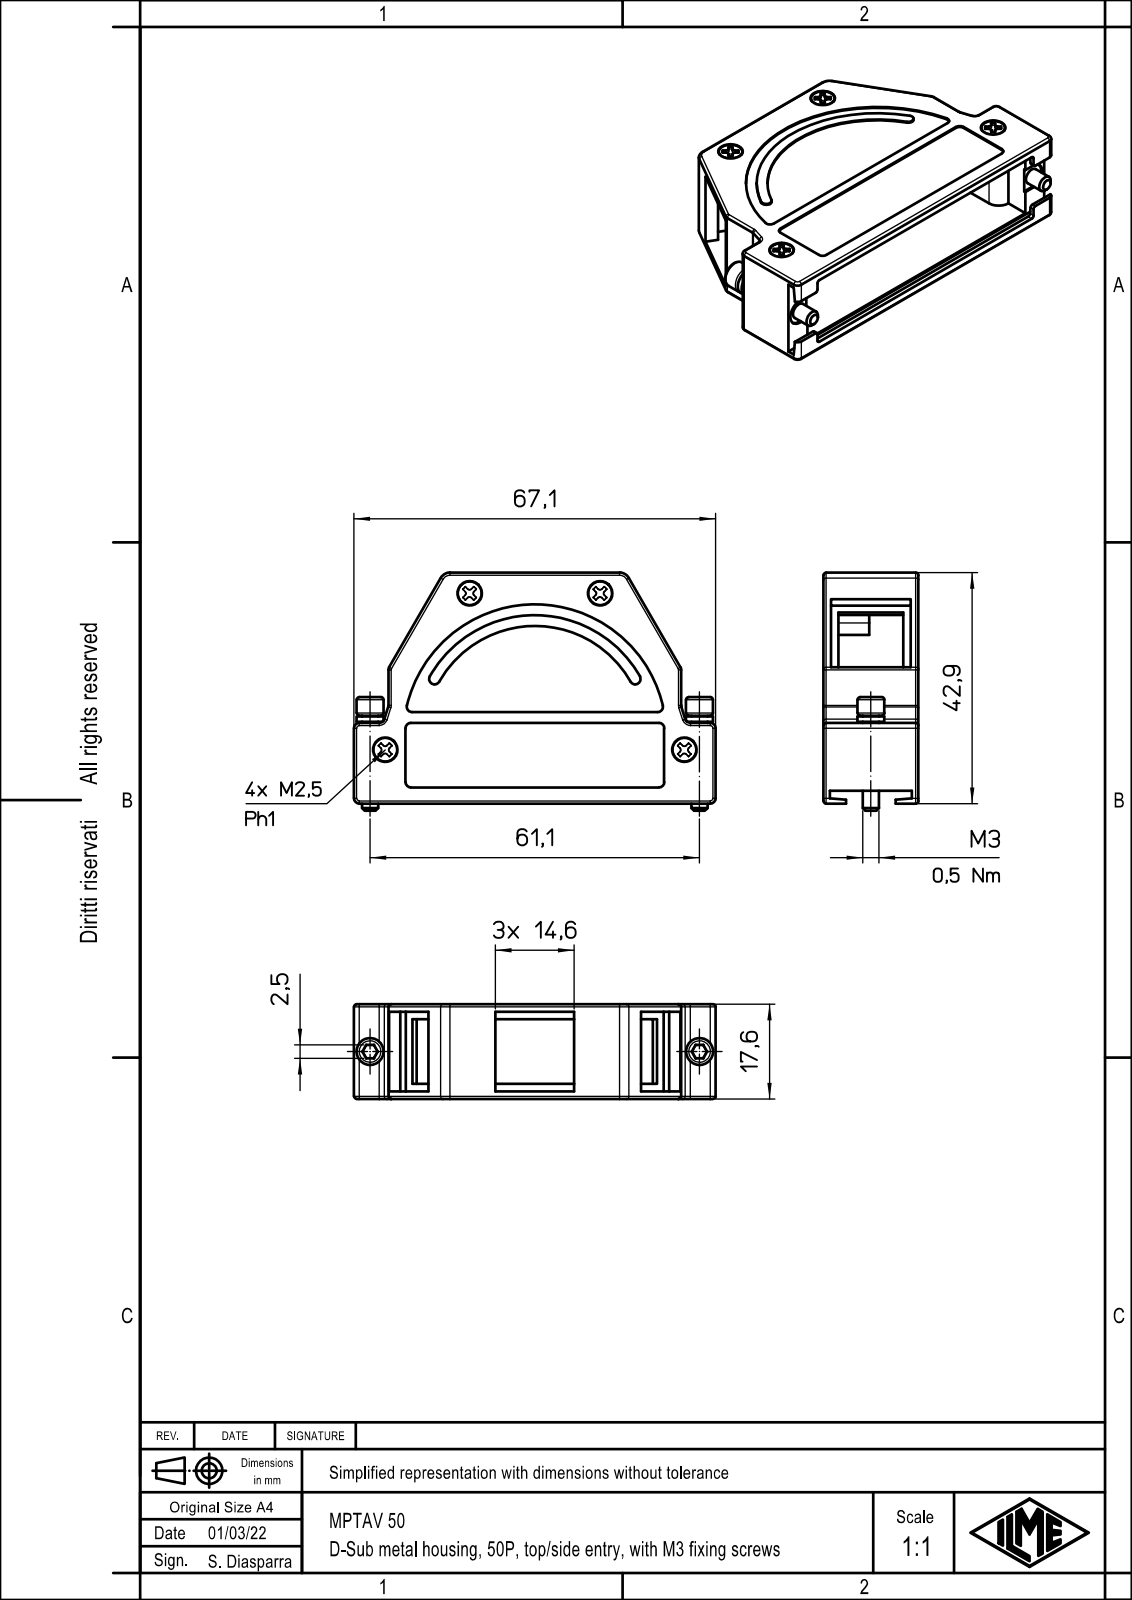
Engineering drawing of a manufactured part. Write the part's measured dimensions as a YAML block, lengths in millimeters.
part_name: "MPTAV_50"
step_written_by: "Creo Elements/Direct Modeling 20.1B 02-Apr-2019 (C) Parametric Technology GmbH (AUTOMOTIVE_DESIGN)"
units: millimeters
bodies: {solids: 1, faces: 717, planar: 166, cylindrical: 211, other: 340}
overall_size: [67.1, 44.2, 17.6]
volume: 11764
surface_area: 13494
round_bosses_or_shafts:
  - {diameter: 5, count: 2}
  - {diameter: 3, count: 2}
partial_cylinders:
  - {radius: 0.5, count: 46}
  - {radius: 1, count: 18}
  - {radius: 2, count: 2}
  - {radius: 2.55, count: 2}
  - {radius: 2.2, count: 1}
  - {radius: 20.4, count: 1}
  - {radius: 22.4, count: 1}
  - {radius: 24.4, count: 1}
face_to_face_distances: [1.3, 15.9, 17.4, 1.5, 16.1, 14.6, 17.2, 17.6, 1.2, 16.2]
